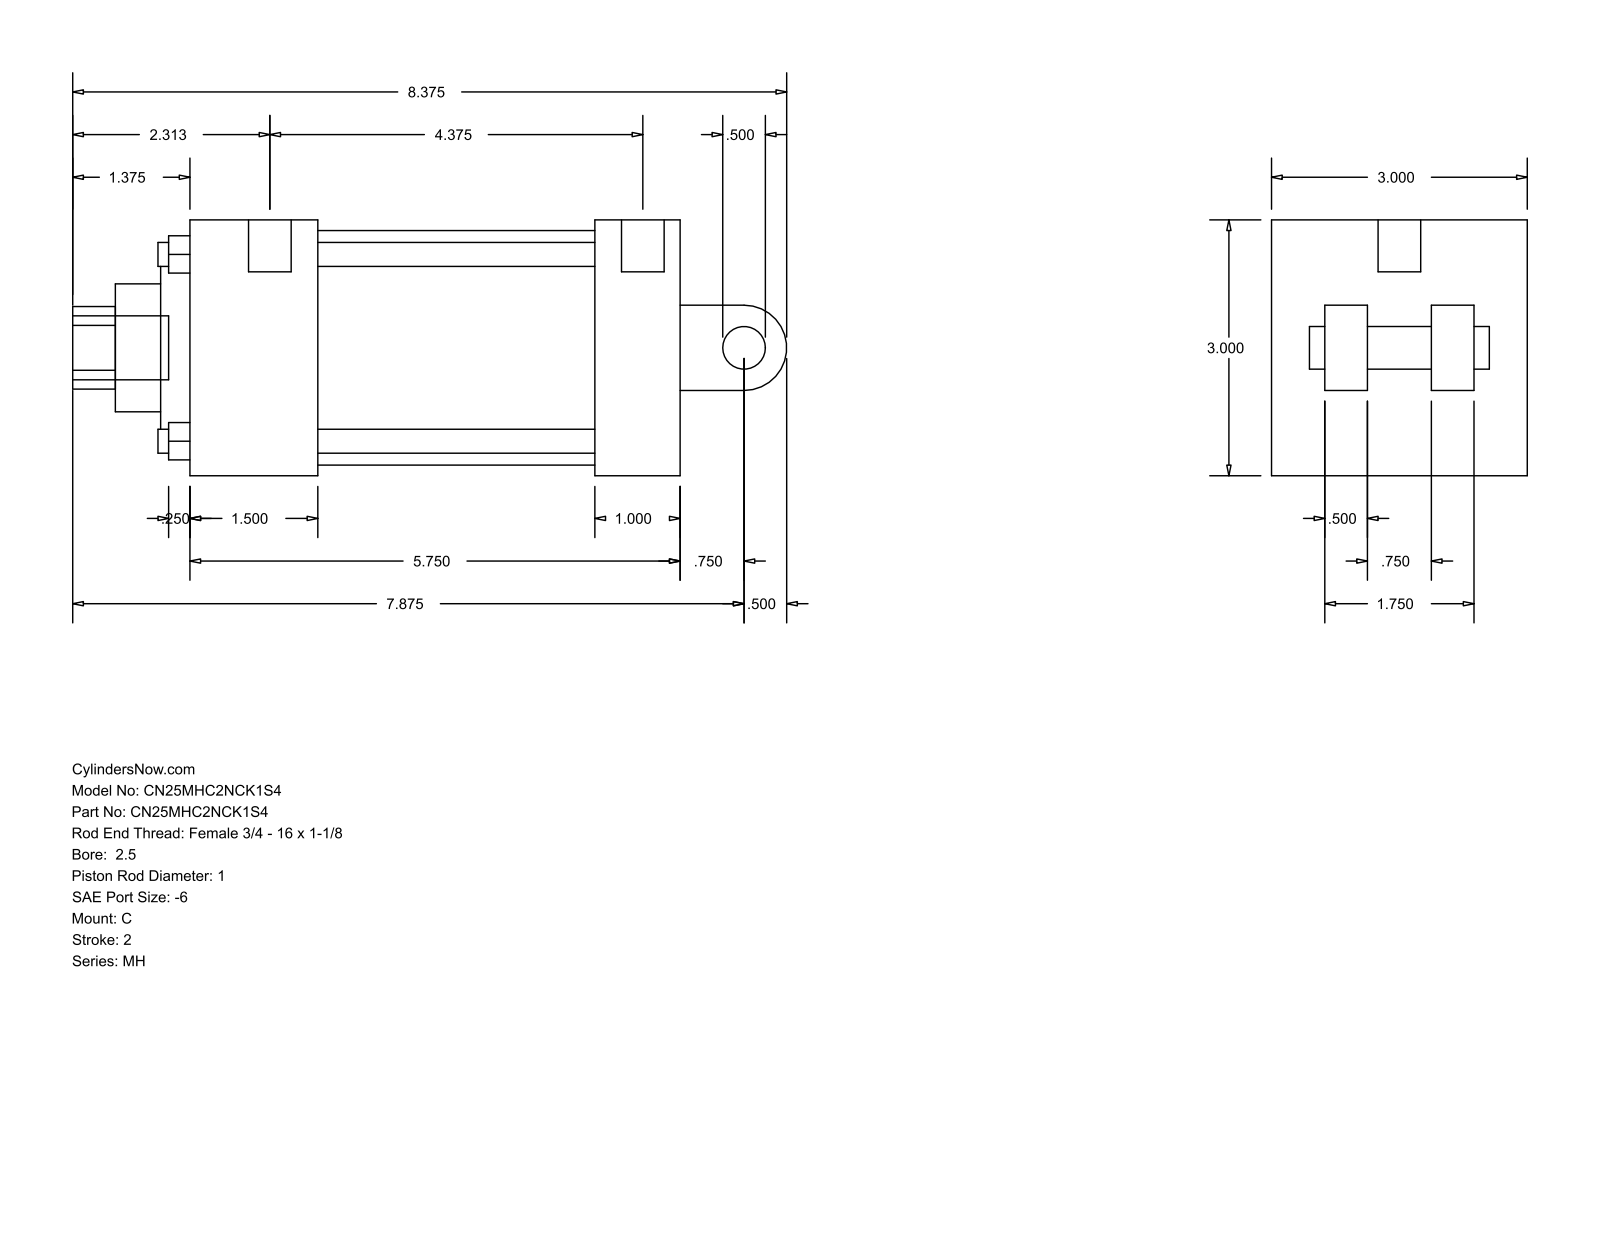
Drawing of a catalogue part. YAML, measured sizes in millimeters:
part_name: "MH_C__0250_1"
step_written_by: "GSSL Pune (CONFIG_CONTROL_DESIGN)"
units: millimeters
bodies: {solids: 0, faces: 101, planar: 71, cylindrical: 30, other: 0}
overall_size: [212.72, 76.2, 76.2]
round_holes:
  - {diameter: 7.14, count: 4}
  - {diameter: 5.56, count: 2}
  - {diameter: 12.7, count: 1}
  - {diameter: 25.4, count: 1}
  - {diameter: 38.1, count: 1}
  - {diameter: 60.33, count: 1}
  - {diameter: 69.85, count: 1}
round_bosses_or_shafts:
  - {diameter: 12.7, count: 2}
  - {diameter: 5.56, count: 2}
  - {diameter: 19.05, count: 1}
partial_cylinders:
  - {radius: 12.29, count: 1}
  - {radius: 12.7, count: 1}
face_to_face_distances: [76.2, 25.4, 146.05, 15.87, 60.33, 120.65, 38.11, 82.54, 107.94, 12.7]
hole_center_spacings: [39.33, 55.62, 78.66, 3.18]
